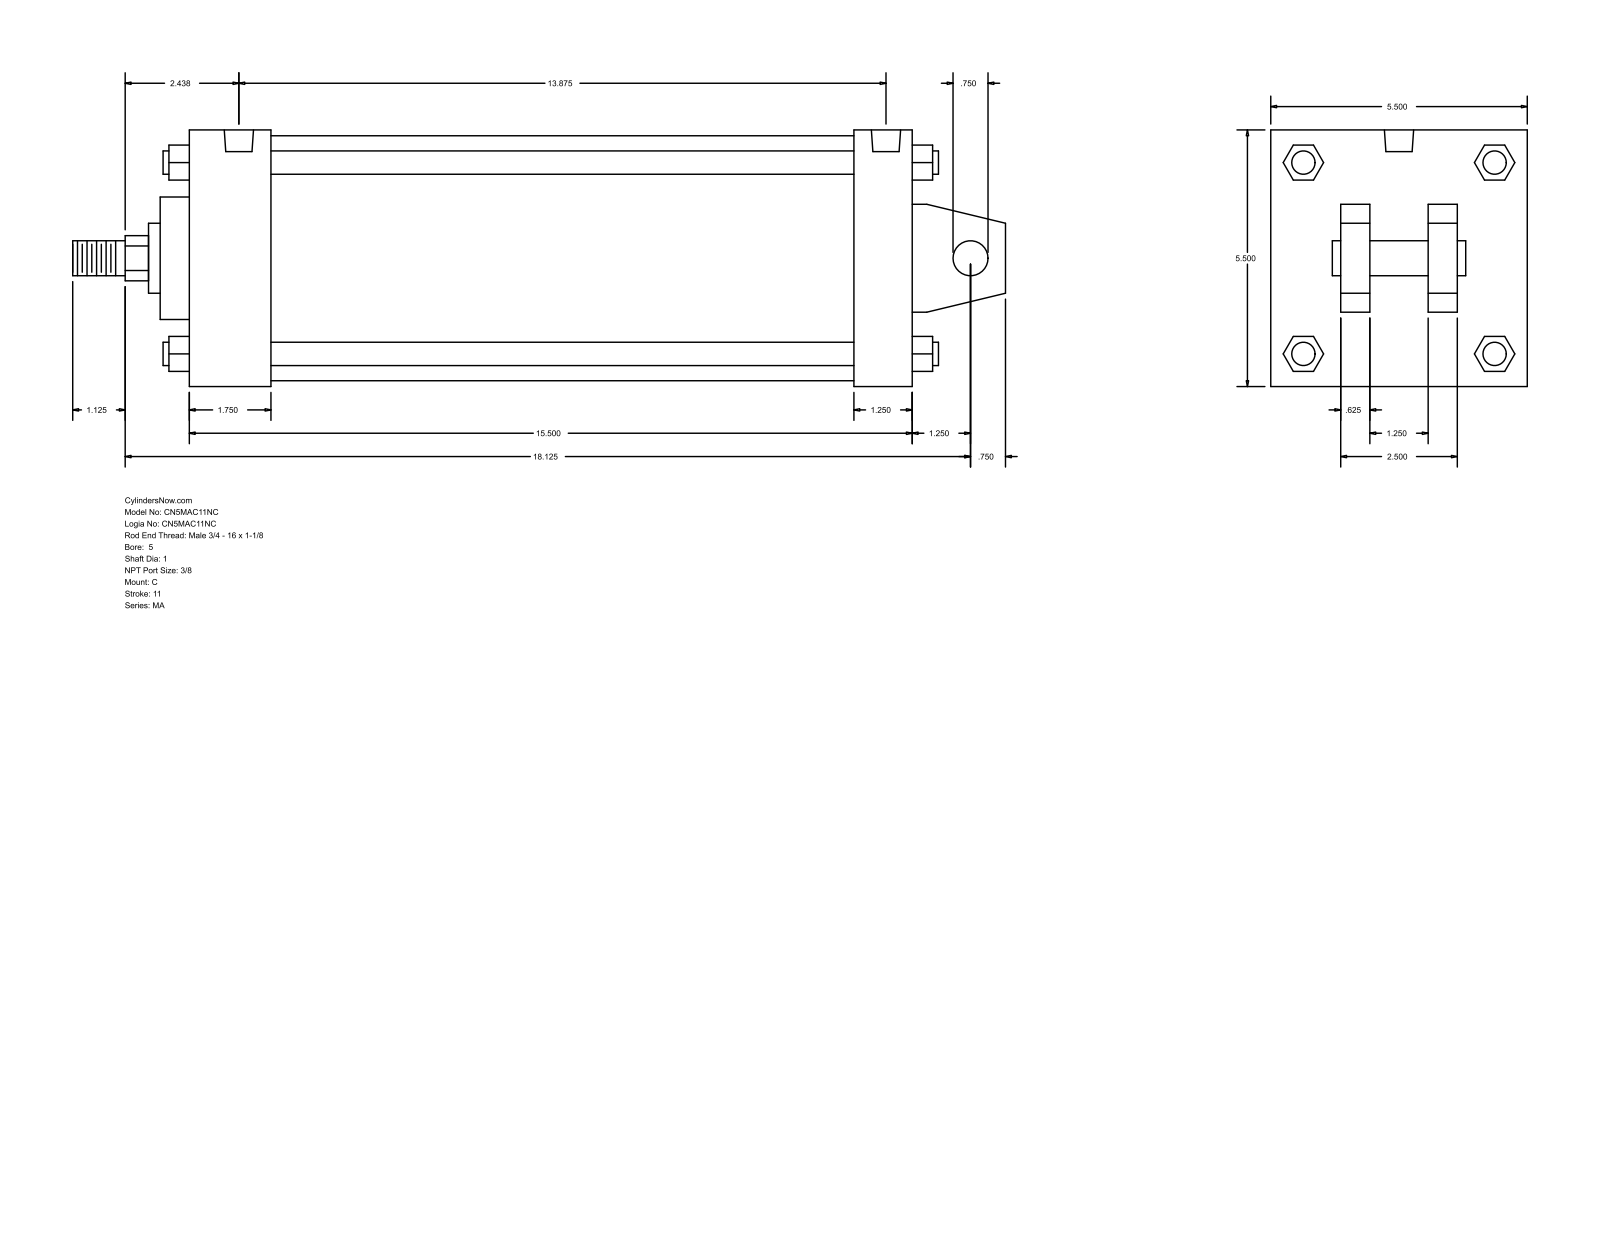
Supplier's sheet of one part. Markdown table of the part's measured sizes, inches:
| quantity | value |
| --- | --- |
| part name | MA_C__0500_1 |
| STEP written by | GSSL Pune (CONFIG_CONTROL_DESIGN) |
| units | inches |
| bodies | 0 solids, 141 faces (109 planar, 32 cylindrical, 0 other) |
| overall size | 20 × 5.5 × 5.5 |
| round holes (diameter × count) | 0.437 × 4, 0.627 × 2 |
| round bosses / shafts (diameter × count) | 0.5 × 4, 0.75 × 2, 5.25 × 1, 2.625 × 1, 1.5 × 1, 1 × 1 |
| partial cylindrical surfaces (radius × count) | 0.484 × 1 |
| main face-to-face distances | 5.5, 15.5, 0.625, 14.25, 1.25, 1.75, 12.5, 13.75, 1.5, 4 |
| hole center spacings | 13.5, 0.187, 0.188, 13.687, 13.688, 13.875 |
